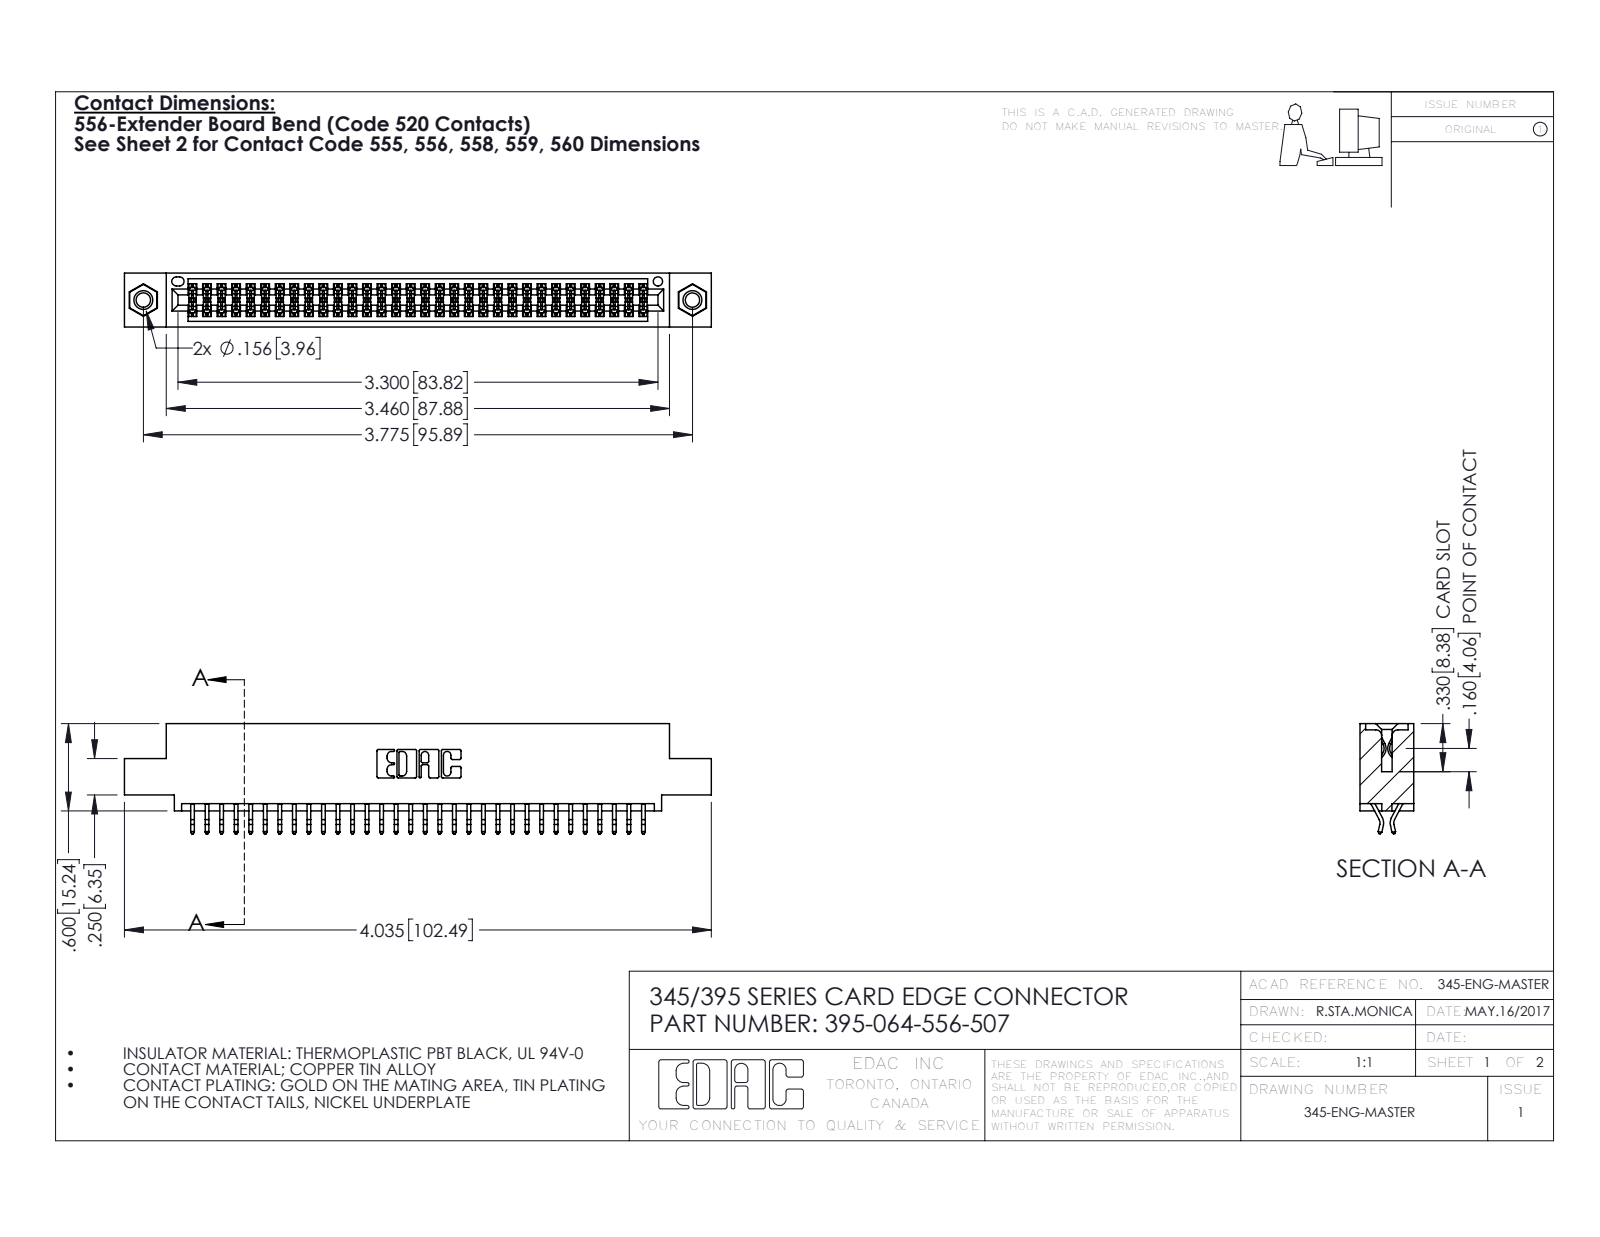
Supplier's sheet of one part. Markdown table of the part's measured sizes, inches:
| quantity | value |
| --- | --- |
| part name | 345-250-001_345-250-005-103; 345-292-001_556 Tail; 345 Part_0.110 Offset - 0.156 Dia-TI; 395-064-556-507 |
| STEP written by | SolidWorks 2016 (CONFIG_CONTROL_DESIGN) |
| units | inches |
| bodies | 67 solids, 3774 faces (2484 planar, 1274 cylindrical, 16 other) |
| overall size | 4.035 × 0.757 × 0.37 |
| volume | 0.596 in³ |
| surface area | 22.19 in² |
| round holes (diameter × count) | 0.098 × 2, 0.125 × 2, 0.156 × 2, 0.064 × 1 |
| round bosses / shafts (diameter × count) | 0.155 × 2 |
| partial cylindrical surfaces (radius × count) | 0.006 × 96, 0.01 × 22, 0.007 × 6, 0.031 × 6, 0.026 × 3, 0.01 × 2, 0.014 × 2, 0.019 × 2 |
| main face-to-face distances | 0.072, 0.298, 0.37, 0.2, 0.025, 0.098, 0.272, 0.225, 0.175, 0.149 |
| hole center spacings | 0.27, 3.54, 3.775 |
